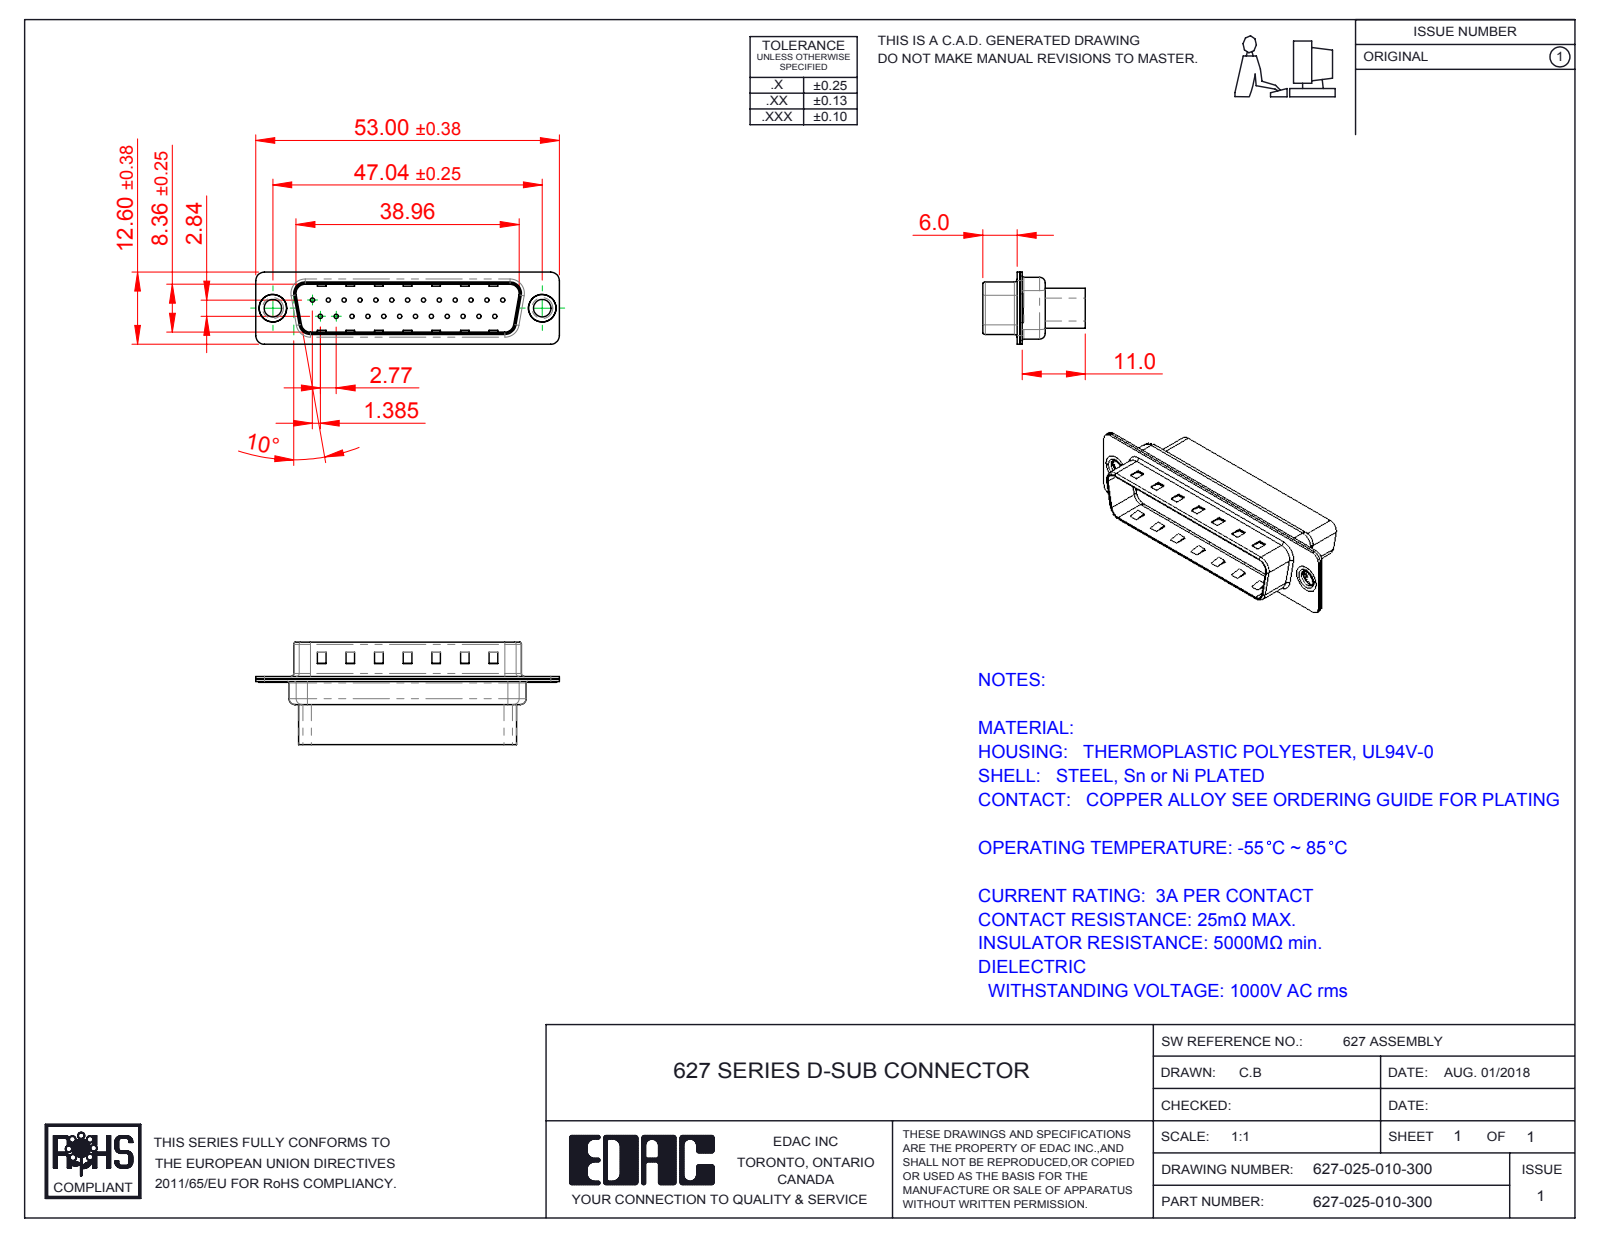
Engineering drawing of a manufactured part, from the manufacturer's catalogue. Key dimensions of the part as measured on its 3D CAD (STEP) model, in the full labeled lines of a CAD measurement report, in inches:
Part name (STEP PRODUCT): 627 Thru Hole Rivet; 627 Shell Rear_25 Contacts; 627 Shell Front_25 Contacts; 627 Housing_25 HP (+1 more)
STEP written by: SolidWorks 2016 (CONFIG_CONTROL_DESIGN)
Units: inches
Bodies: 5 solids, 550 faces (221 planar, 271 cylindrical, 58 other)
Overall size (bounding box): 2.087 × 0.705 × 0.496
Volume: 0.216 in³ · Surface area: 10.2 in²
Round holes (diameter × count): ⌀0.03 ×25, ⌀0.063 ×25, ⌀0.079 ×25, ⌀0.12 ×2, ⌀0.157 ×2, ⌀0.189 ×2
Round bosses / shafts (diameter × count): ⌀0.197 ×2, ⌀0.193 ×2, ⌀0.14 ×2
Partial cylindrical surfaces — rounded edges, fillets, slot ends (radius × count): R0.059 ×16, R0.079 ×12, R0.02 ×8, R0.063 ×8, R0.01 ×4, R0.024 ×4, R0.026 ×4, R0.035 ×4
Main face-to-face distances: 0.016, 0.018, 0.032, 0.377, 0.027, 0.302, 0.035, 0.043, 0.318, 0.345
Hole centre spacings: 0.124, 0.327, 0.109, 0.218, 0.436, 0.654, 0.198, 0.198
